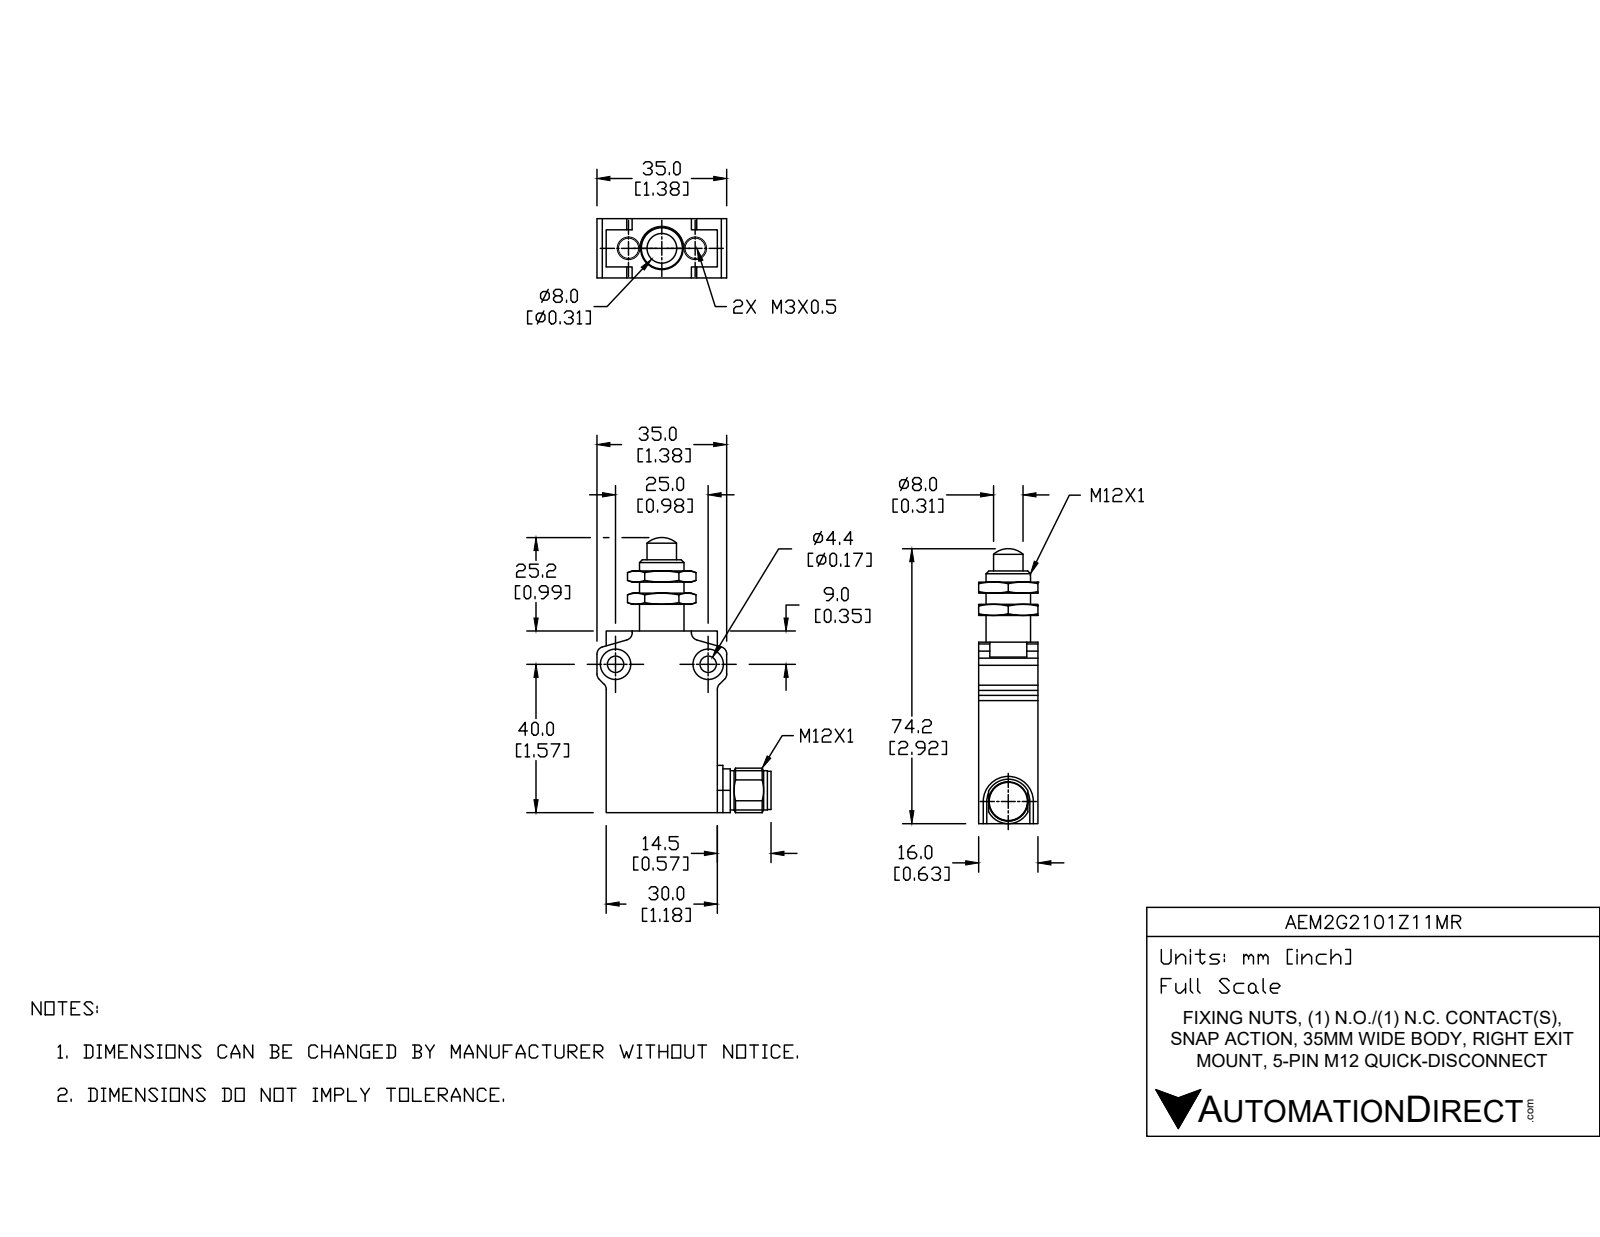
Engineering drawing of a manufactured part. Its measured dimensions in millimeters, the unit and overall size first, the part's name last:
Units: millimetres
Overall size (bounding box): 77.2 × 46.5 × 17.9
Round holes (diameter × count): ⌀3 ×2, ⌀4.4 ×2, ⌀8.2 ×2, ⌀8.1 ×1, ⌀12 ×1
Round bosses / shafts (diameter × count): ⌀12 ×1, ⌀10.6 ×1, ⌀10.3 ×1, ⌀8 ×1
Partial cylindrical surfaces — rounded edges, fillets, slot ends (radius × count): R2 ×8, R6.5 ×1
Main face-to-face distances: 16, 30, 12, 3, 6, 52, 9, 47.2, 4.8, 2.5
Hole centre spacings: 9.5, 19, 25
Volume: 28 530 mm³ · Surface area: 10 860 mm²
Bodies: 6 solids, 174 faces (67 planar, 49 cylindrical, 58 other)
Part name (STEP PRODUCT): AEM2G2101Z11MR
STEP written by: SolidWorks 2019 (AUTOMOTIVE_DESIGN)
